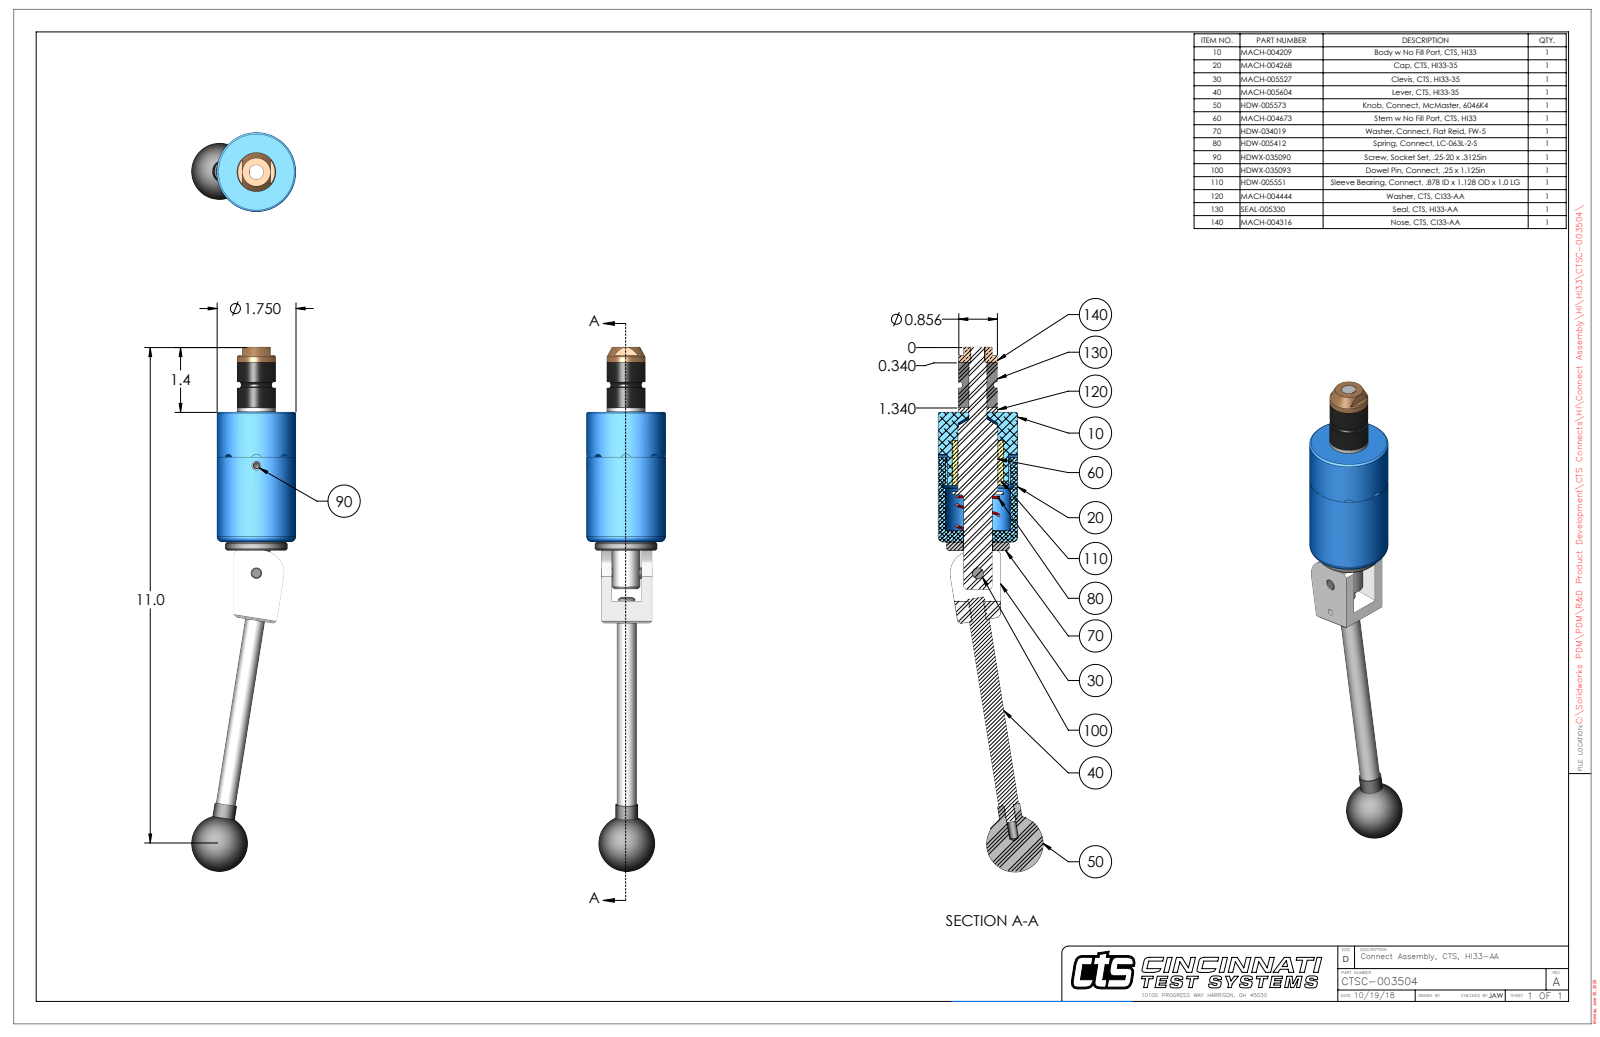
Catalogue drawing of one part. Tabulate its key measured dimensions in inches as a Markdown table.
| quantity | value |
| --- | --- |
| part name | CTSC-003504 |
| STEP written by | SolidWorks 2023 (AUTOMOTIVE_DESIGN) |
| units | inches |
| bodies | 9 solids, 248 faces (94 planar, 95 cylindrical, 59 other) |
| overall size | 11.613 × 2.312 × 1.75 |
| volume | 10.9 in³ |
| surface area | 61.7 in² |
| round holes (diameter × count) | 0.201 × 2, 0.313 × 2, 0.15 × 1, 0.249 × 1, 0.251 × 1, 0.39 × 1, 0.397 × 1, 0.403 × 1, 0.635 × 1, 0.656 × 1, 1.419 × 1 |
| round bosses / shafts (diameter × count) | 0.375 × 2, 0.312 × 2, 0.25 × 2, 1.75 × 1, 1.38 × 1, 0.856 × 1, 0.625 × 1, 0.5 × 1 |
| partial cylindrical surfaces (radius × count) | 0.125 × 4, 0.029 × 2, 0.5 × 1, 0.695 × 1, 0.831 × 1 |
| main face-to-face distances | 2.878, 1.12, 0.188, 1.098, 3.066, 1, 0.888, 0.232, 0.232, 0.656 |
| hole center spacings | 0.74, 2.376, 3.116 |
